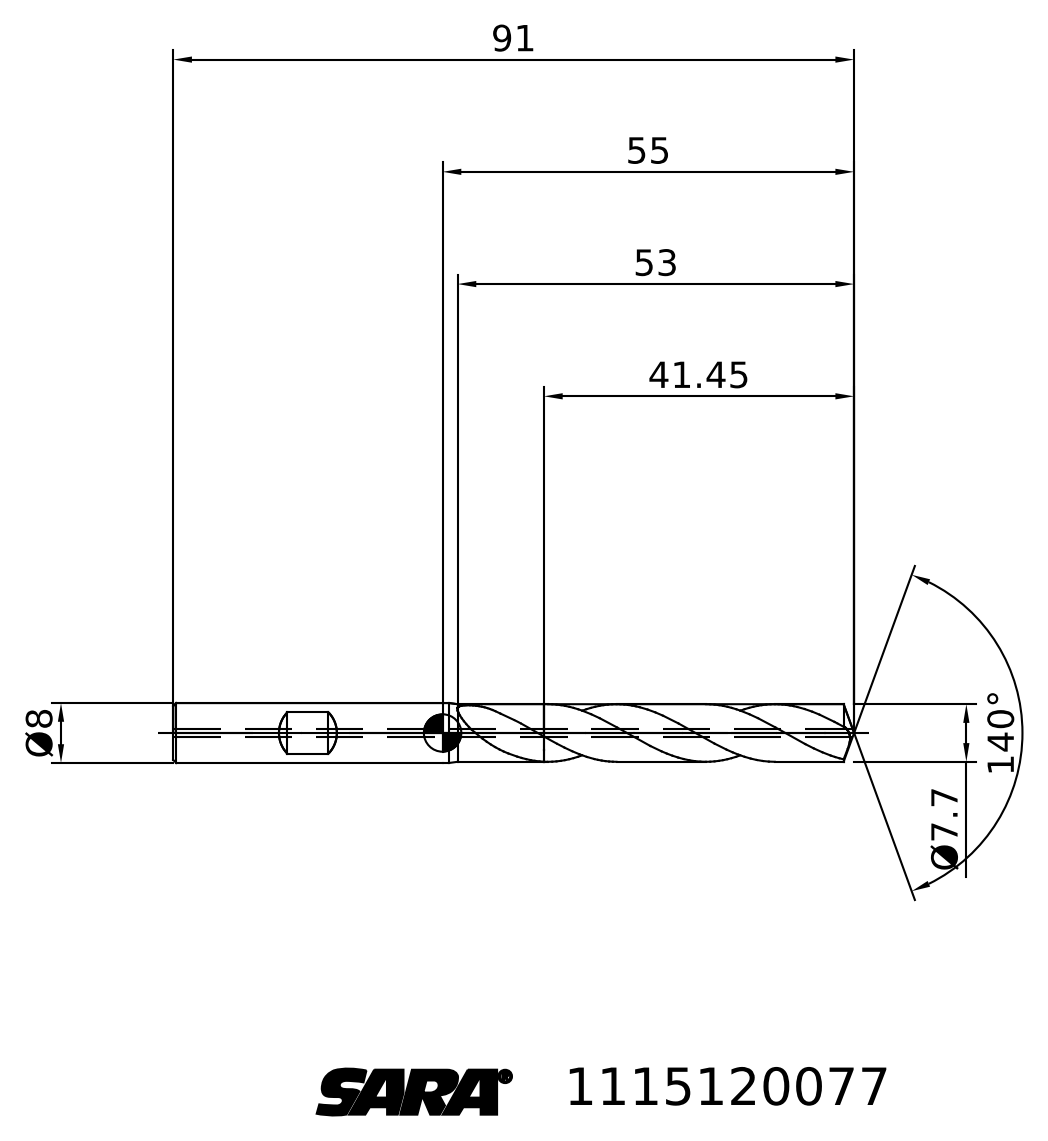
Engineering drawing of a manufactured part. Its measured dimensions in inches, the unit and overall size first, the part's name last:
Units: inches
Overall size (bounding box): 3.583 × 0.804 × 0.446
Main face-to-face distances: 1.951
Volume: 0.214 in³ · Surface area: 3.816 in²
Bodies: 2 solids, 30 faces (6 planar, 0 cylindrical, 24 other)
STEP written by: TDM (AUTOMOTIVE_DESIGN)
